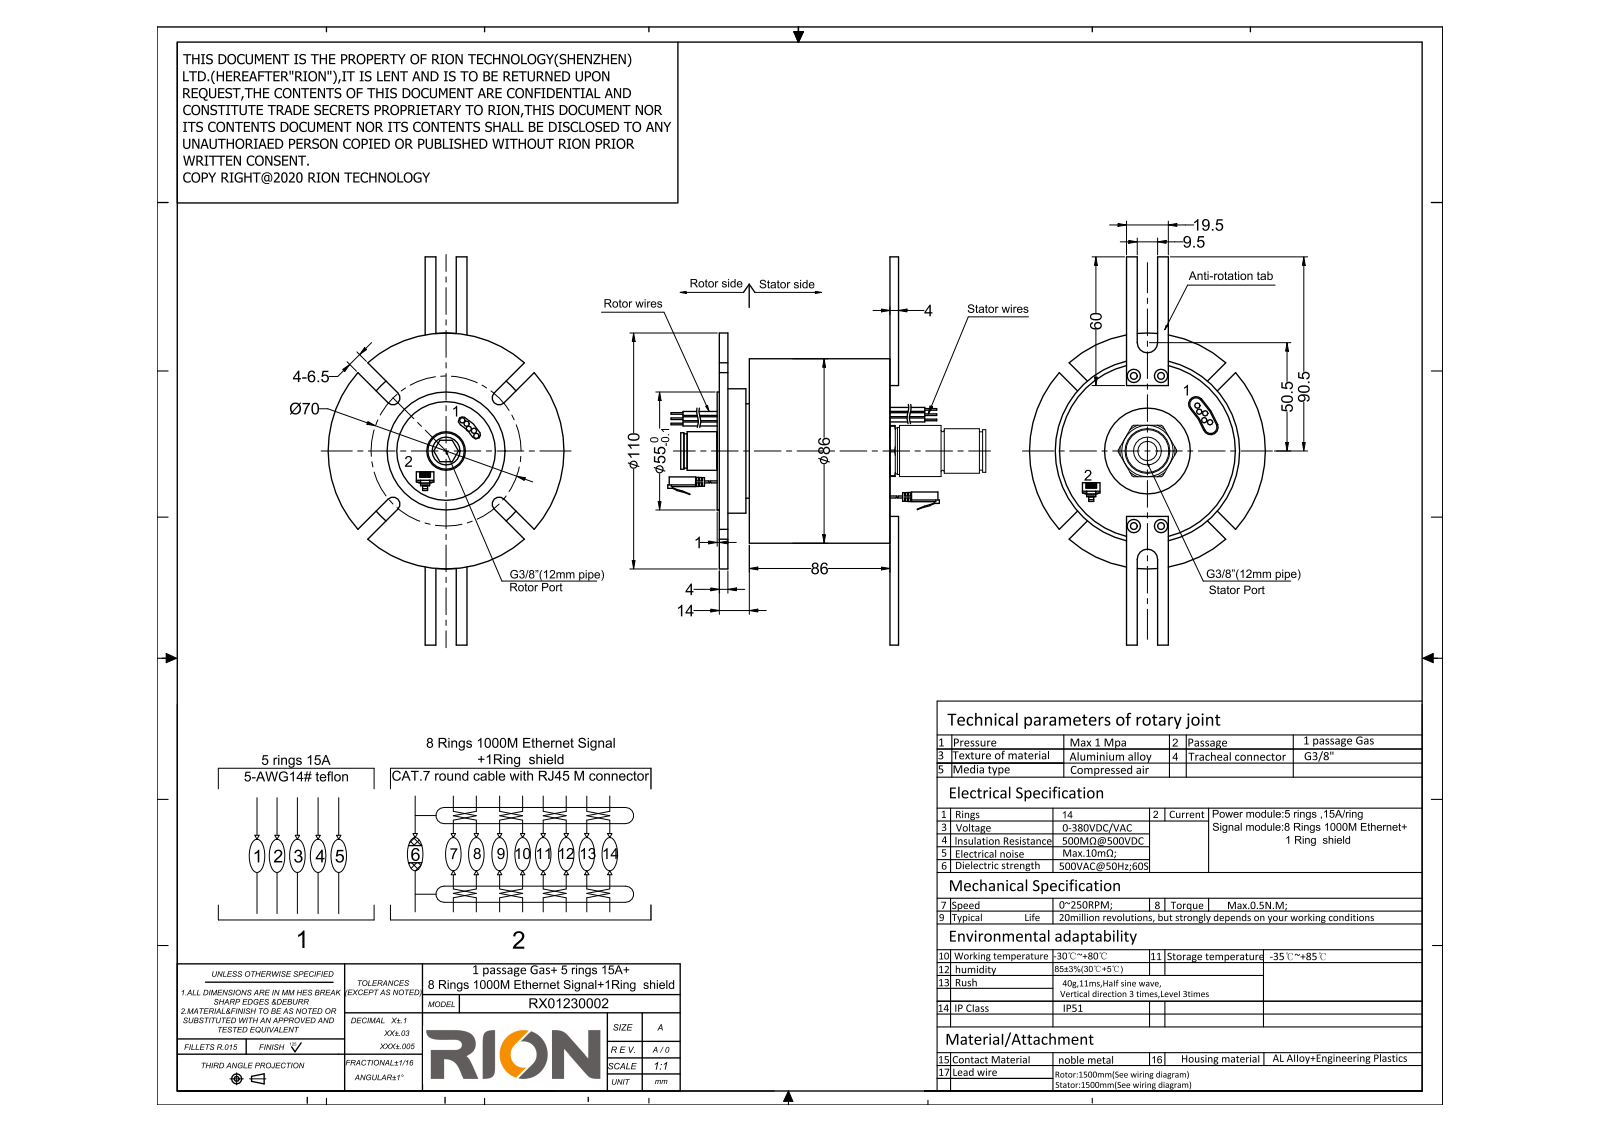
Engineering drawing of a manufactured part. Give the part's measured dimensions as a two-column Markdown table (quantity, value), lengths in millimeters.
| quantity | value |
| --- | --- |
| part name | KQ2S12-03S; RX01230002; KSH12-03S |
| STEP written by | SolidWorks 2014 (CONFIG_CONTROL_DESIGN) |
| units | millimeters |
| bodies | 3 solids, 277 faces (104 planar, 135 cylindrical, 38 other) |
| overall size | 181 × 159.1 × 110 |
| volume | 564 002 mm³ |
| surface area | 84 288 mm² |
| round holes (diameter × count) | 2.5 × 4, 3.2 × 4, 9 × 1, 10 × 1, 13 × 1, 15.25 × 1, 25.4 × 1, 30.8 × 1, 46 × 1, 82 × 1 |
| round bosses / shafts (diameter × count) | 2.5 × 10, 6.5 × 2, 110 × 1, 86 × 1, 81.8 × 1, 58 × 1, 55 × 1, 44 × 1 |
| partial cylindrical surfaces (radius × count) | 2 × 8, 3.25 × 4, 4.75 × 2, 14 × 1, 18 × 1 |
| main face-to-face distances | 4, 100, 96, 14, 10, 86, 5.4, 1.4, 8.6, 94.6 |
| hole center spacings | 35.57, 12.7, 70, 71.14 |
